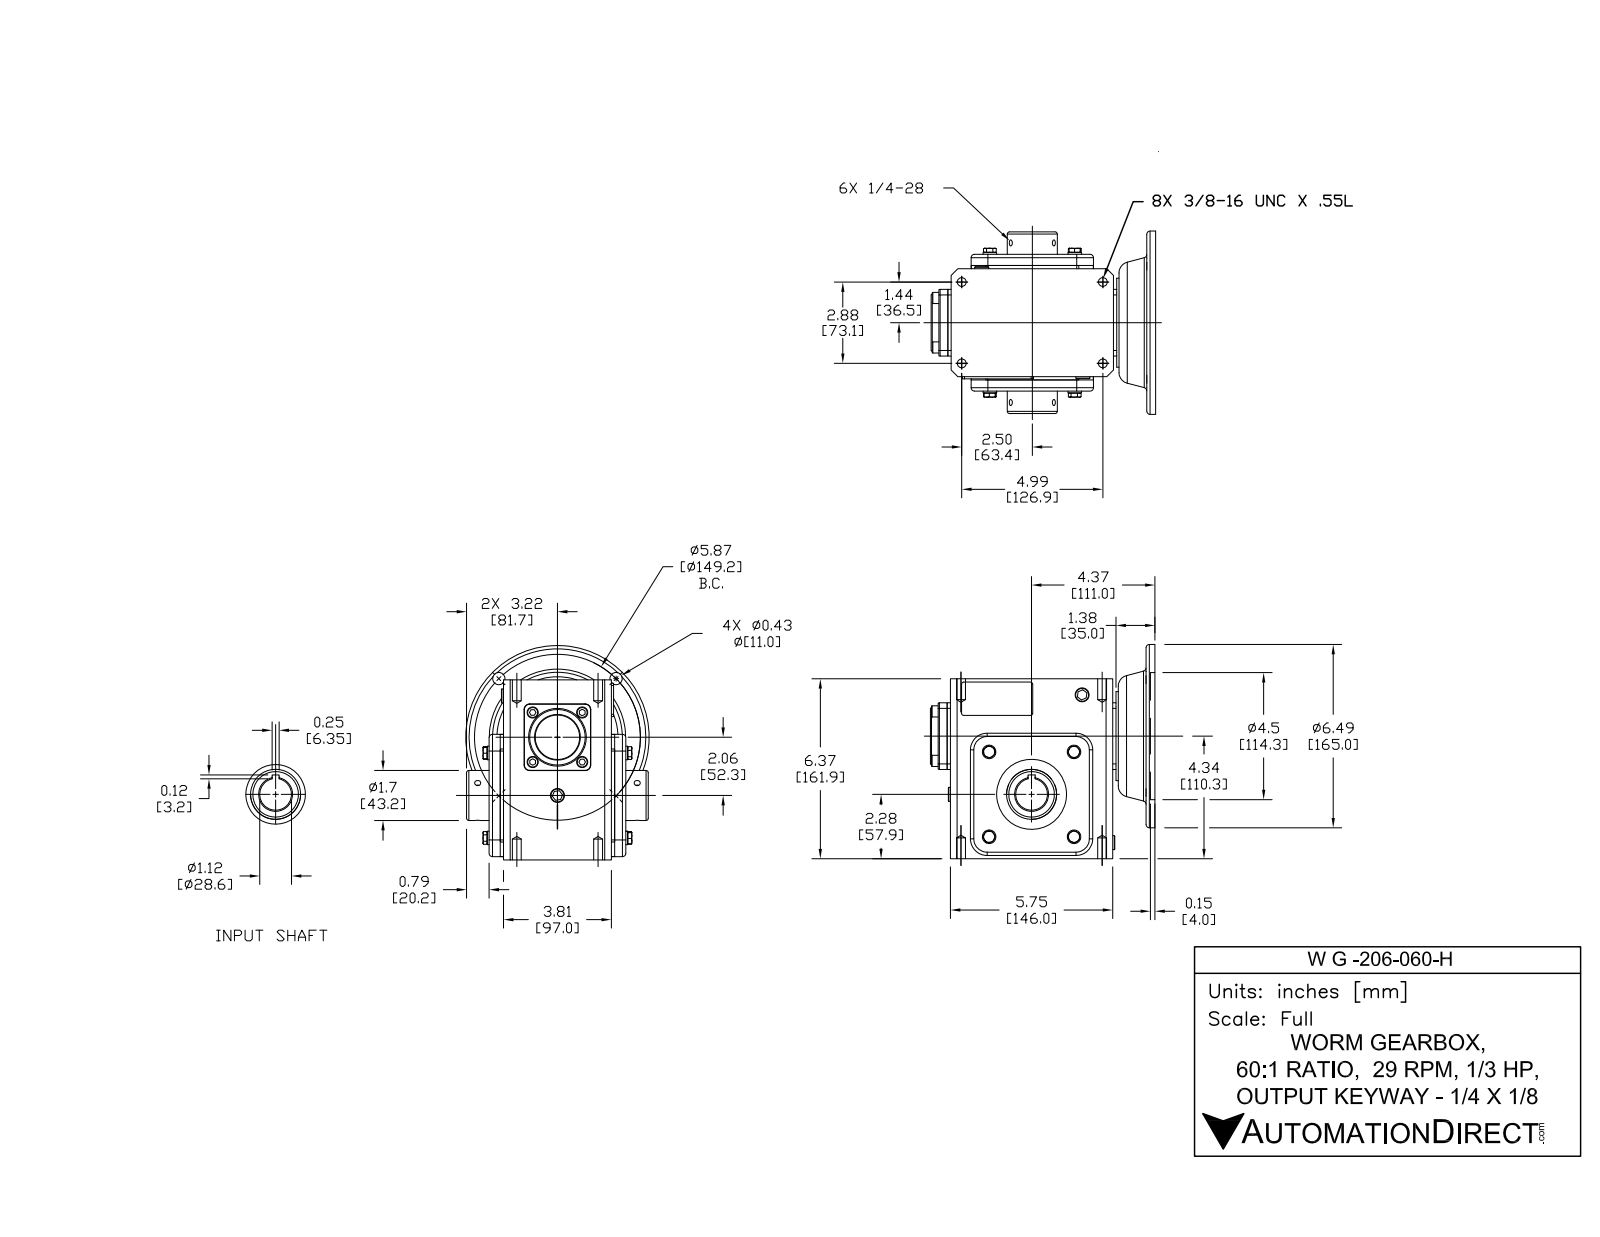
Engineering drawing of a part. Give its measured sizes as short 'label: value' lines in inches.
name: WG-206-060-H
written by: SolidWorks 2015 (CONFIG_CONTROL_DESIGN)
unit: in
bodies: 45 solids, 628 faces (304 planar, 198 cylindrical, 126 other)
size: 7.953 × 7.591 × 6.496
volume: 171 in³; area: 463.1 in²
holes: 6× ⌀0.213, 4× ⌀0.313, 4× ⌀0.406, 1× ⌀0.591, 1× ⌀0.625, 1× ⌀1.125, 1× ⌀1.457, 1× ⌀1.772, 1× ⌀2.402, 1× ⌀3.543, 1× ⌀4.5
bosses: 8× ⌀0.394, 4× ⌀0.48, 1× ⌀6.496, 1× ⌀3.15, 1× ⌀2.047, 1× ⌀1.575, 1× ⌀1.181, 1× ⌀1.142
rounds: 8× R0.079, 8× R0.118, 4× R0.197, 4× R0.591, 2× R0.02, 2× R0.039, 1× R2.717
face distances: 0.118, 4.055, 0.394, 4.331, 3.937, 0.512, 4.449, 6.375, 5.866, 1.181
hole spacings: 2.858, 2.937, 4.154, 4.943, 5.65, 2.077, 2.88, 4.631
